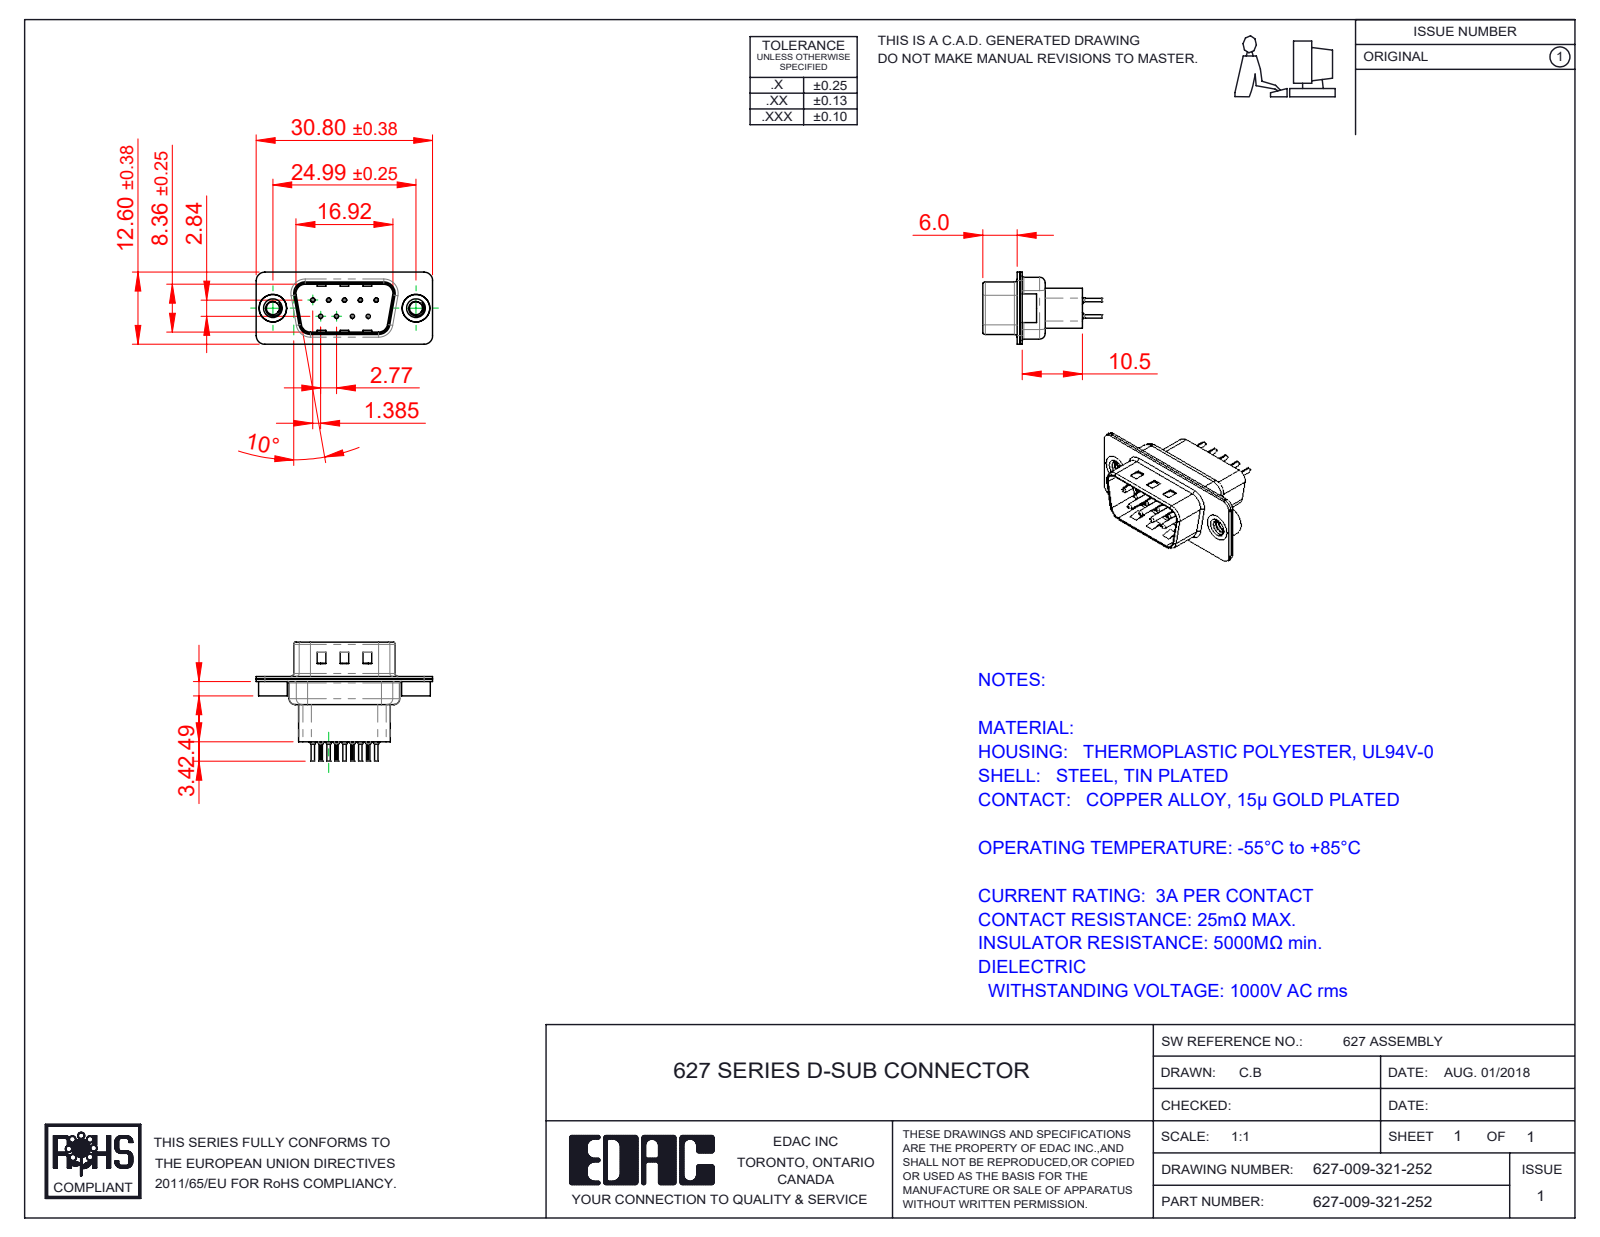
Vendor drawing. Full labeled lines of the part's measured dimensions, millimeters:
Part name (STEP PRODUCT): 627 Housing_09 HP; 627 Contact Row 1_21H; 627 Shell Front_09 Contacts; 627 Contact Row 2_21H (+3 more)
STEP written by: SolidWorks 2020 (CONFIG_CONTROL_DESIGN)
Units: millimetres
Bodies: 14 solids, 1182 faces (323 planar, 460 cylindrical, 399 other)
Overall size (bounding box): 30.8 × 20.8 × 12.6
Volume: 1 767 mm³ · Surface area: 4 688 mm²
Round holes (diameter × count): ⌀0.2 ×9, ⌀0.35 ×9, ⌀1.1 ×9, ⌀1.6 ×9, ⌀2.26 ×2, ⌀4 ×2, ⌀4.8 ×2
Round bosses / shafts (diameter × count): ⌀2 ×9, ⌀1.5 ×9, ⌀0.75 ×9, ⌀0.6 ×9, ⌀5 ×2, ⌀4.9 ×2
Partial cylindrical surfaces — rounded edges, fillets, slot ends (radius × count): R0.1 ×18, R1.5 ×18, R2 ×12, R0.5 ×8, R1.6 ×8, R0.25 ×4, R0.6 ×4, R0.65 ×4
Main face-to-face distances: 0.45, 0.4, 0.9, 0.82, 9.58, 1.4, 1.5, 0.68, 7.68, 1.08
Hole centre spacings: 3.16, 2.77, 5.54, 5.03, 5.04, 8.31, 7.48, 7.49
